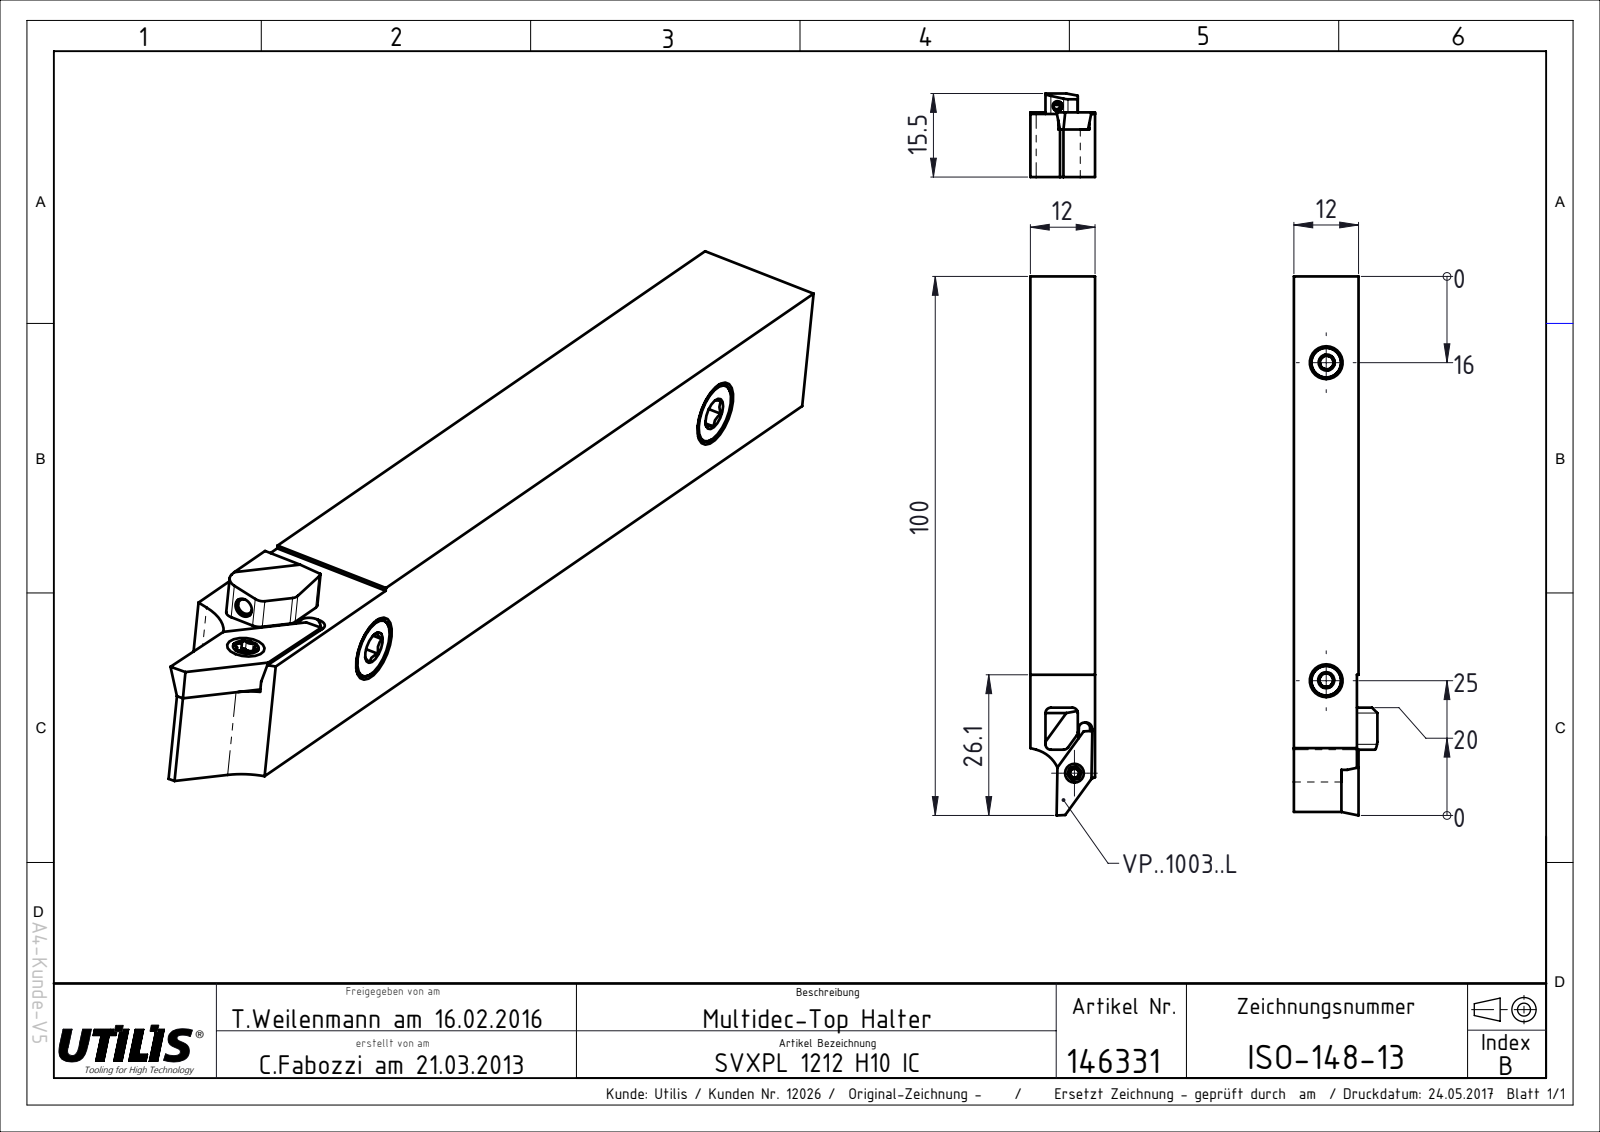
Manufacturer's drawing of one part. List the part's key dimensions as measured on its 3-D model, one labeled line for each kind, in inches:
Part name (STEP PRODUCT): ISO-148-13
STEP written by: SolidWorks 2015 (AUTOMOTIVE_DESIGN)
Units: inches
Bodies: 0 solids, 62 faces (52 planar, 9 cylindrical, 1 other)
Overall size (bounding box): 3.937 × 0.61 × 0.472
Partial cylindrical surfaces — rounded edges, fillets, slot ends (radius × count): R0.039 ×5, R0.24 ×2, R0.041 ×1
Main face-to-face distances: 0.472, 0.461, 0.11, 0.362, 3.15, 0.346, 0.236, 0.126, 0.21, 0.61
